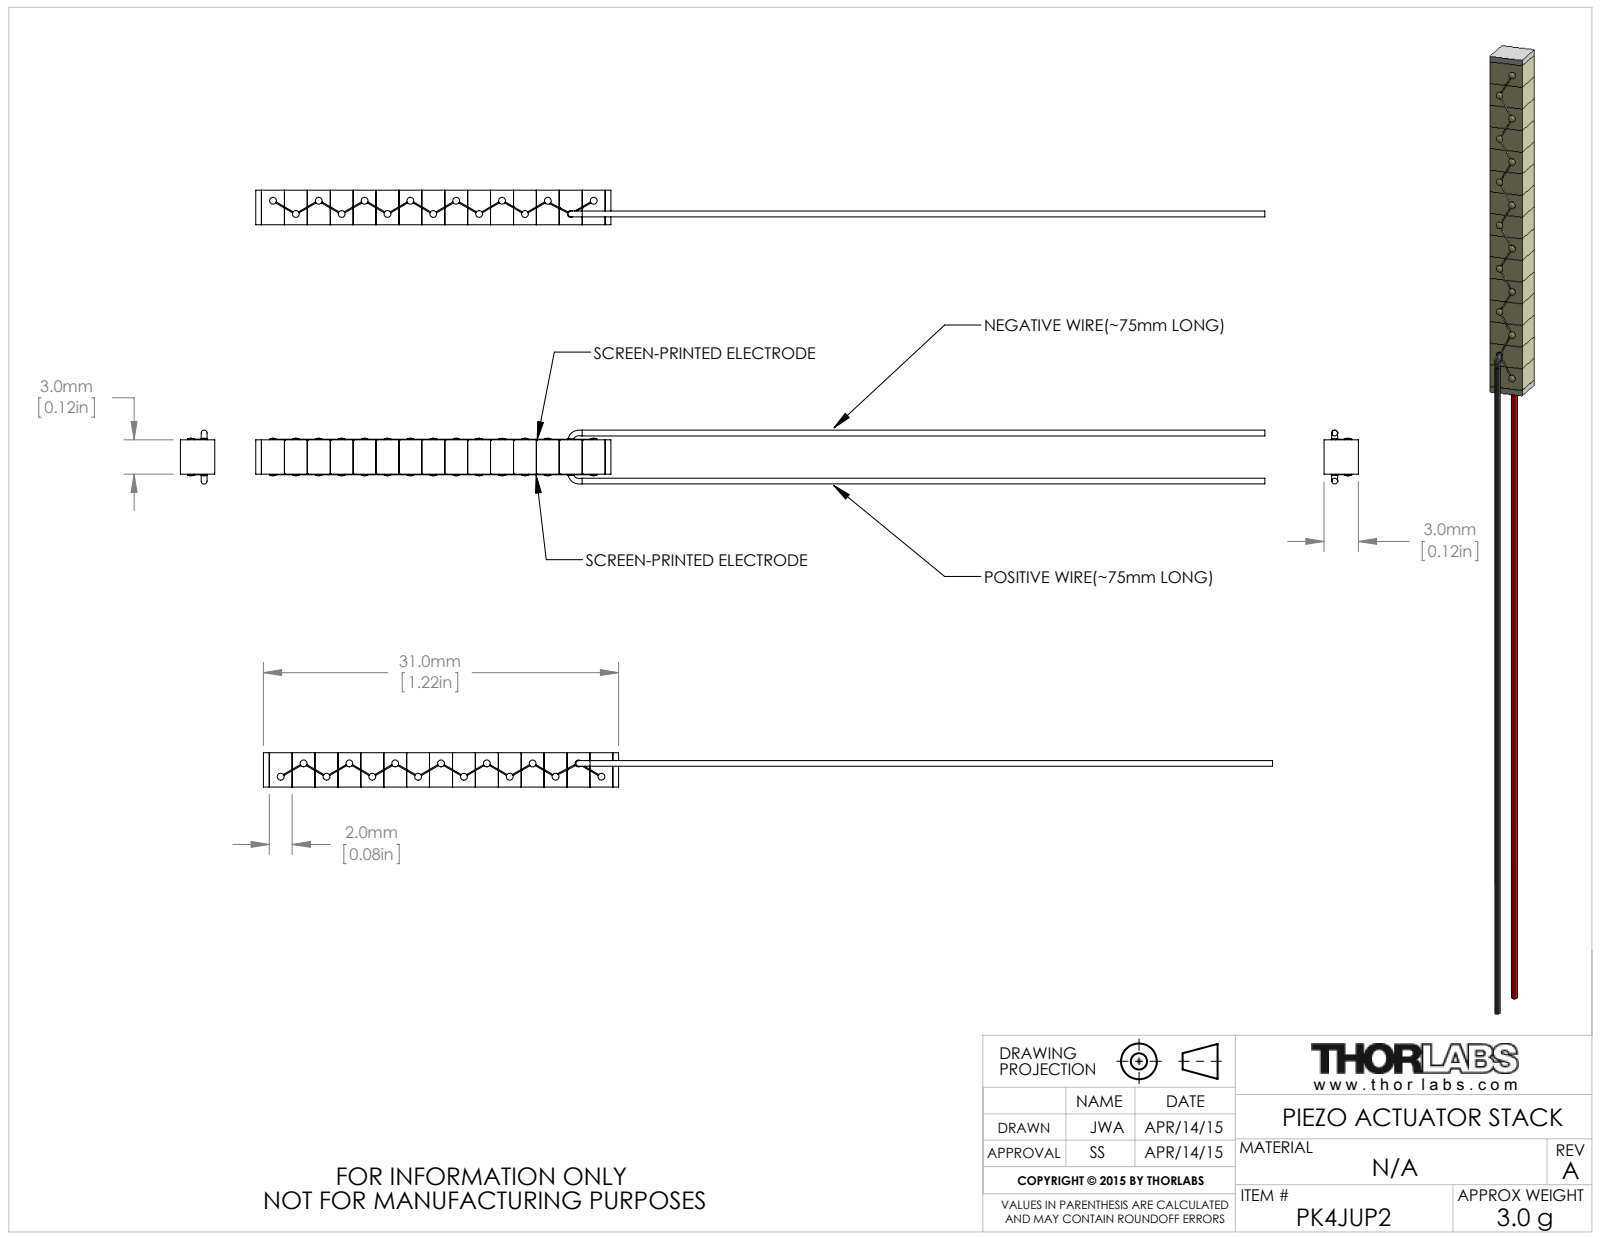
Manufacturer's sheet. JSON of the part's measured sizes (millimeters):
{"part_name": "CTN002960", "step_written_by": "SolidWorks 2014 (AUTOMOTIVE_DESIGN)", "units": "millimeters", "bodies": {"solids": 20, "faces": 313, "planar": 121, "cylindrical": 126, "other": 66}, "overall_size": [88.1, 4.72, 3], "volume_mm3": 304, "surface_area_mm2": 893, "round_bosses_or_shafts": [[0.6, 15]], "face_to_face_distances": [2, 4, 6, 8, 10, 3, 12, 14, 16, 18]}
